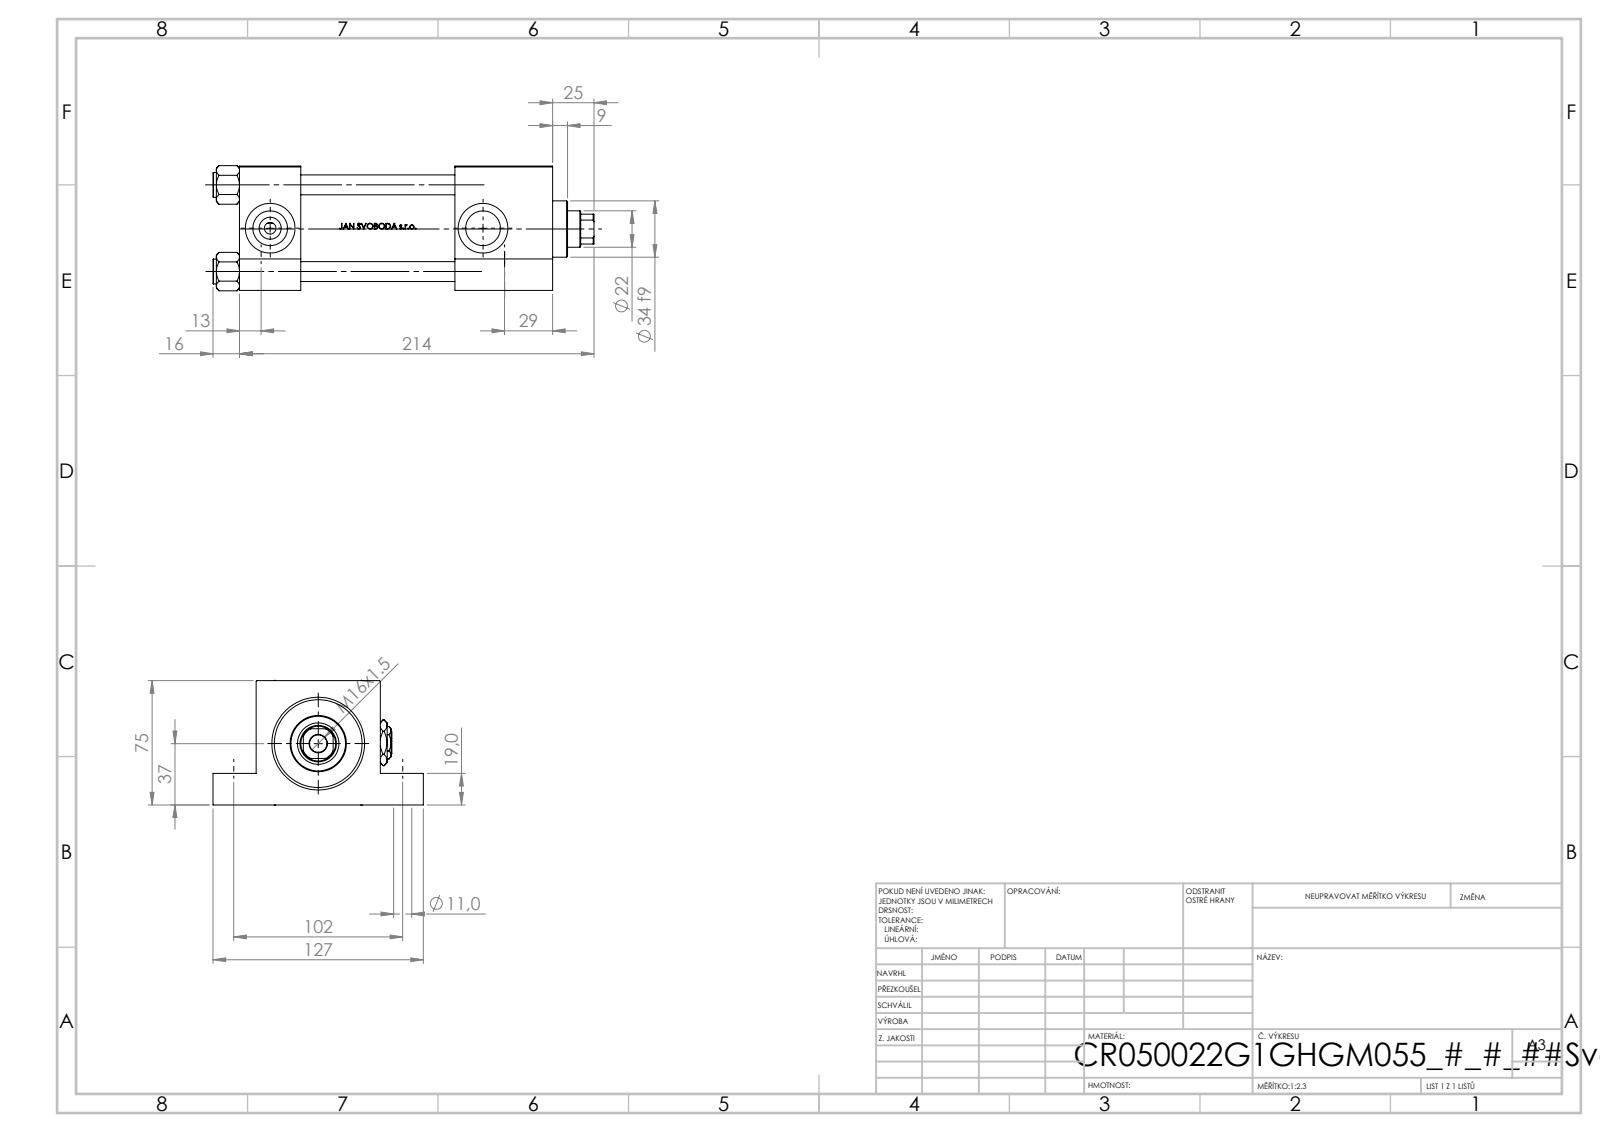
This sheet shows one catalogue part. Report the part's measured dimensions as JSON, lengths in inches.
{"part_name": "Zatka_pro_OIL_PORT; V215_VC_A; V215CR_G_Body; NUT_M5_G (+2 more)", "step_written_by": "SolidWorks 2019 (CONFIG_CONTROL_DESIGN)", "units": "inches", "bodies": {"solids": 12, "faces": 1134, "planar": 454, "cylindrical": 128, "other": 552}, "overall_size": [9.055, 5, 2.974], "volume_in3": 48.76, "surface_area_in2": 280, "round_holes": [[0.433, 4], [0.472, 4], [0.276, 2], [0.825, 2], [1.181, 2], [0.413, 1], [0.866, 1], [0.984, 1], [1.614, 1], [1.969, 1], [2.087, 1]], "round_bosses_or_shafts": [[0.591, 4], [2.205, 1], [1.339, 1]], "partial_cylinders_radius": [[0.413, 1]], "face_to_face_distances": [2.953, 1.457, 7.441, 5.984, 0.748, 2.205, 5.118, 3.661, 2.323, 1.024], "hole_center_spacings": [2.059, 1.442, 1.47, 2.912, 4.016, 5.787, 7.044, 5.059]}
